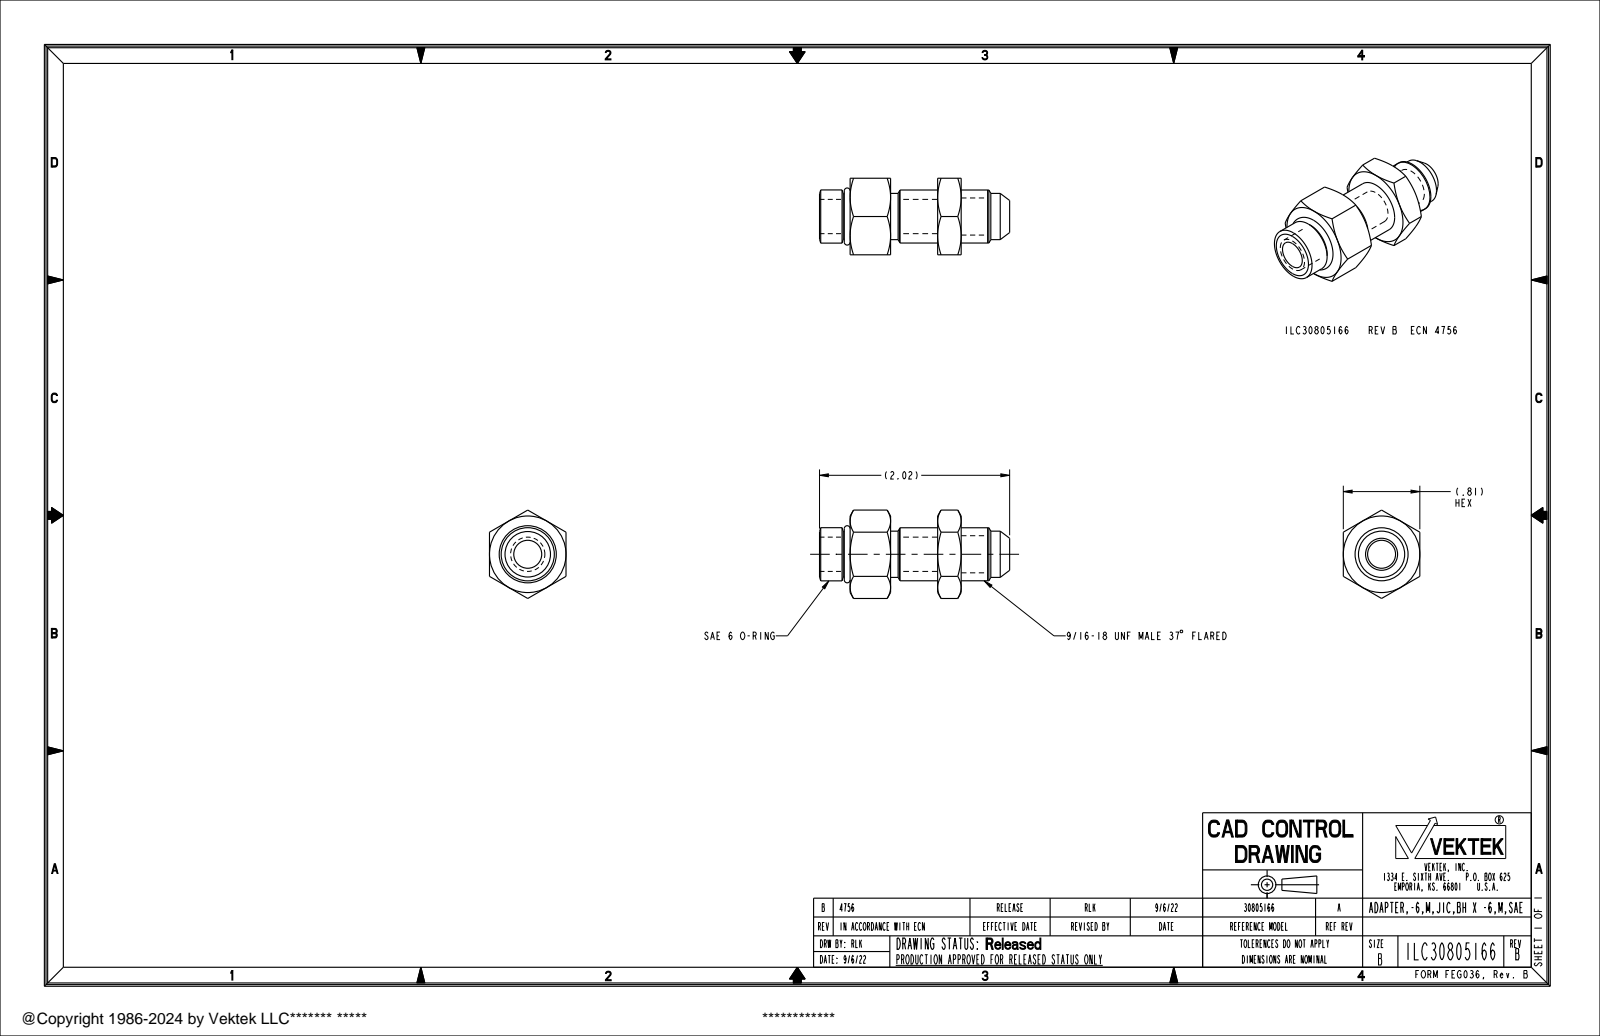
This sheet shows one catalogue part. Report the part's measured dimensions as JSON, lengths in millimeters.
{"part_name": "ILC30805166", "step_written_by": "CREO PARAMETRIC BY PTC INC, 2021164 (AUTOMOTIVE_DESIGN)", "units": "millimeters", "bodies": {"solids": 1, "faces": 78, "planar": 20, "cylindrical": 22, "other": 36}, "overall_size": [51.3, 23.9, 20.7], "volume_mm3": 9130, "surface_area_mm2": 6099, "round_holes": [[7.5, 1]], "round_bosses_or_shafts": [[14.4, 1], [14.3, 1], [12.5, 1], [12.3, 1], [10, 1], [9.2, 1]], "face_to_face_distances": [20.7, 10.9, 20.7, 6.4, 19.1, 30, 12.7, 23.6, 7.1, 13.5]}
